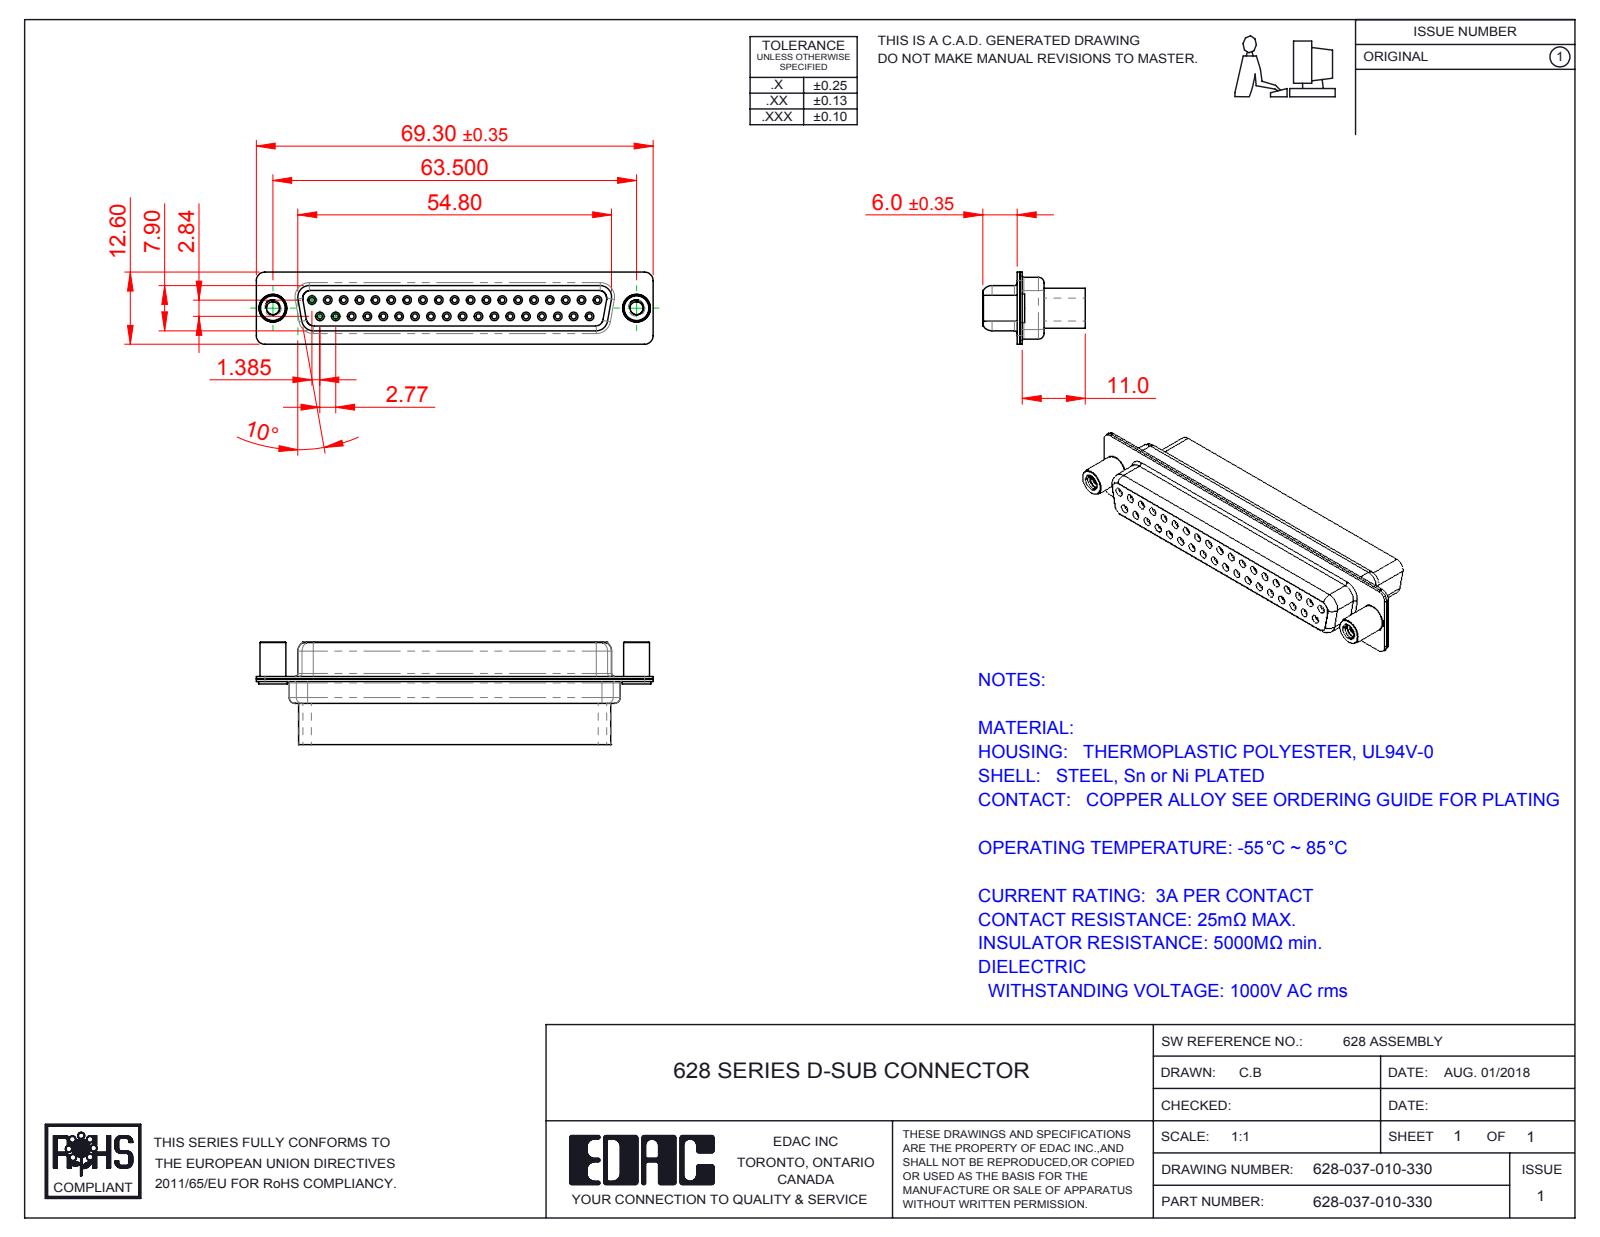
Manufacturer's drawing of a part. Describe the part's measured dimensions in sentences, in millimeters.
The part is named "628 Housing_37 HP; 628 4-40 Threaded Standoff; 628 Shell Rear_37 Contacts; 628-050-010-330 (+1 more)". Its 3-D file was written by "SolidWorks 2016 (CONFIG_CONTROL_DESIGN)". It is 5 solids with 794 faces: 180 planar, 461 cylindrical and 153 other. Overall it measures 69.3 by 17.9 by 12.6 millimeters. Its volume is 6 728 cubic millimeters and its surface area 11 153 square millimeters. Round holes: 37 of diameter 0.9, 37 of diameter 1.5, 37 of diameter 2, 19 of diameter 1.7, 18 of diameter 1.6, 2 of diameter 2.26, 2 of diameter 4, 2 of diameter 4.05, 2 of diameter 4.85. Round bosses or shafts: 2 of diameter 5, 2 of diameter 4.95, 2 of diameter 4.8, 2 of diameter 4.5. Partial cylindrical surfaces (rounded edges, fillets, slot ends): 16 of radius 1.5, 12 of radius 2, 4 of radius 0.25, 4 of radius 0.5, 4 of radius 0.6, 4 of radius 0.65, 4 of radius 0.95, 4 of radius 1. The main face-to-face distances are 0.4, 0.45, 6.6, 7, 1.9, 8.5, 0.85, 7.05, 7.45, 0.9. The hole center spacings are 3.16, 2.77, 5.54, 8.31, 5.04, 7.49, 11.08, 13.85.
